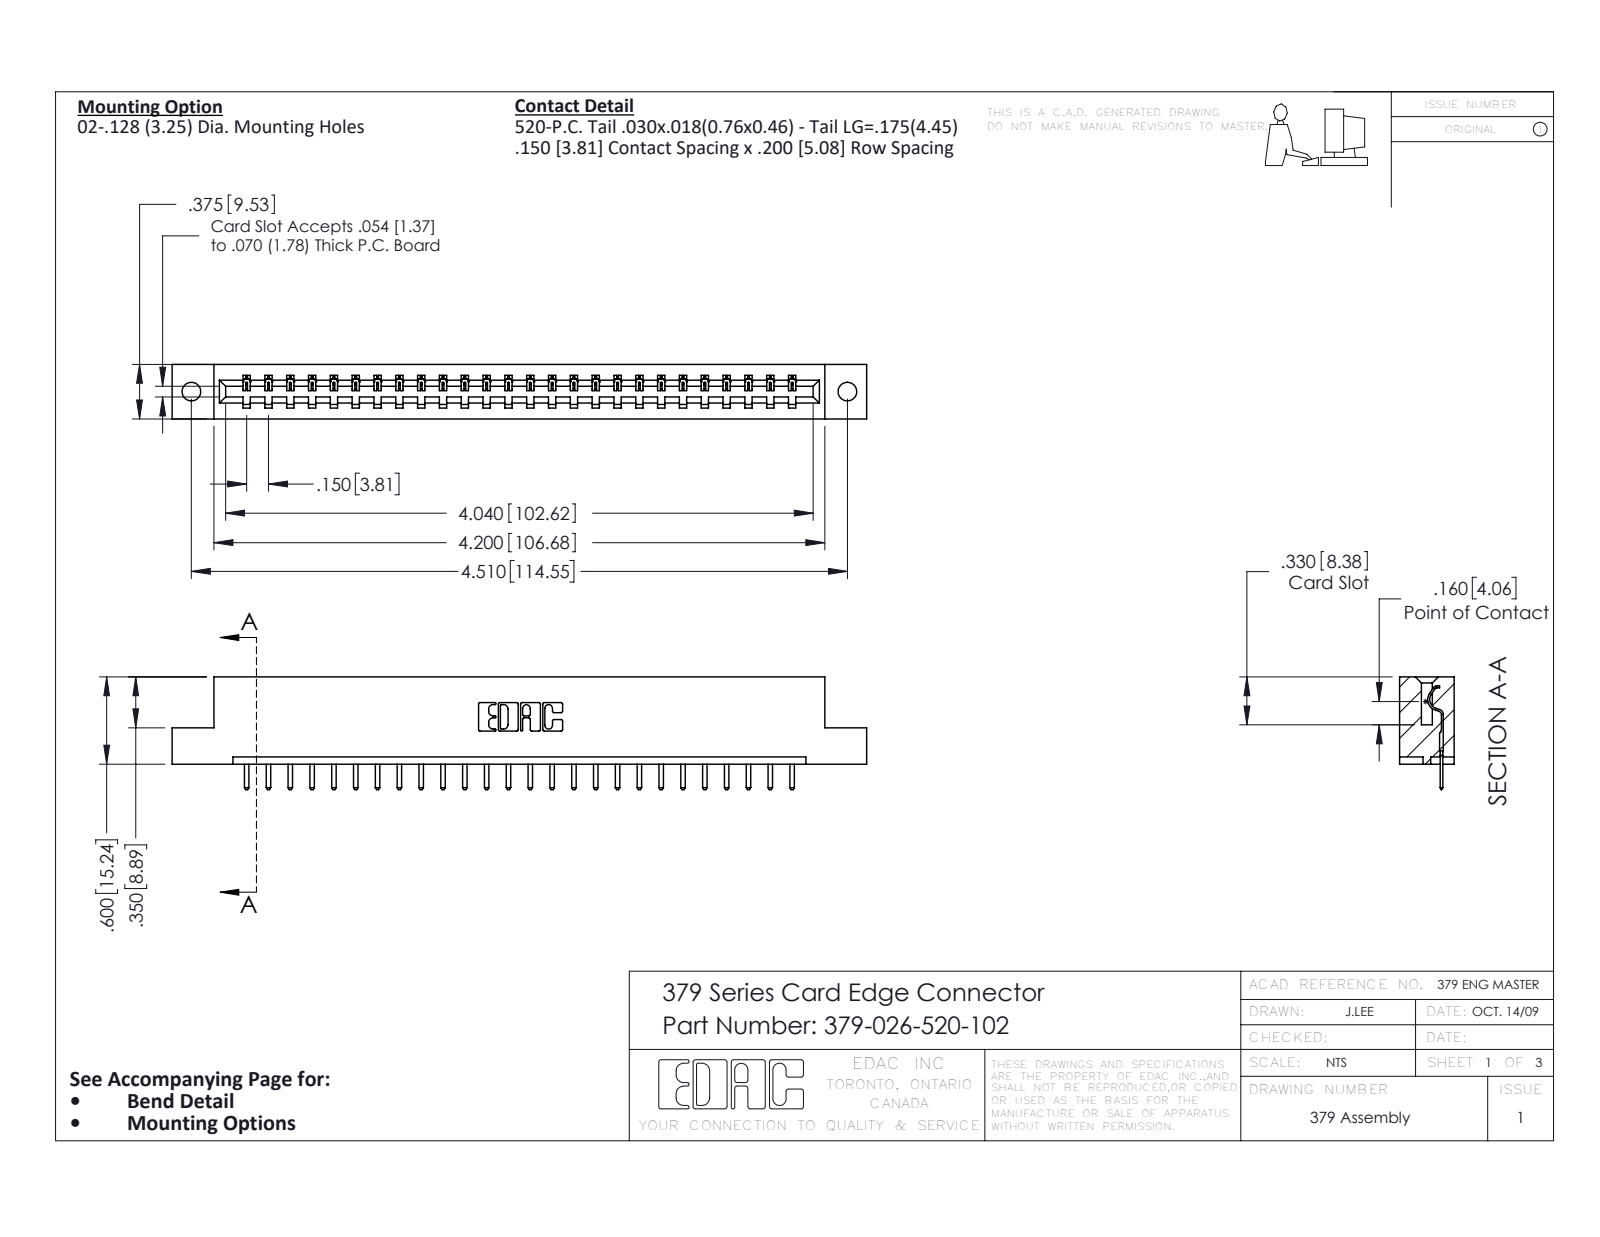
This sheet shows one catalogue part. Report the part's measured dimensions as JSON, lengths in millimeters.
{"part_name": "379-026-520-102; 345-292-001_345-293-120; 379 Part_Flush - .128 Dia", "step_written_by": "SolidWorks 2016 (CONFIG_CONTROL_DESIGN)", "units": "millimeters", "bodies": {"solids": 27, "faces": 1726, "planar": 1214, "cylindrical": 512, "other": 0}, "overall_size": [121.3, 19.7, 9.5], "volume_mm3": 12400, "surface_area_mm2": 12110, "round_holes": [[3.3, 2]], "partial_cylinders_radius": [[0.3, 54], [0.2, 52], [0.3, 22], [0.2, 6], [0.8, 6], [0.7, 3], [0.4, 1], [0.6, 1]], "face_to_face_distances": [7.6, 1.9, 9.5, 5.7, 15.2, 3.8, 5.1, 14, 11.4, 3.8], "hole_center_spacings": [114.6]}
